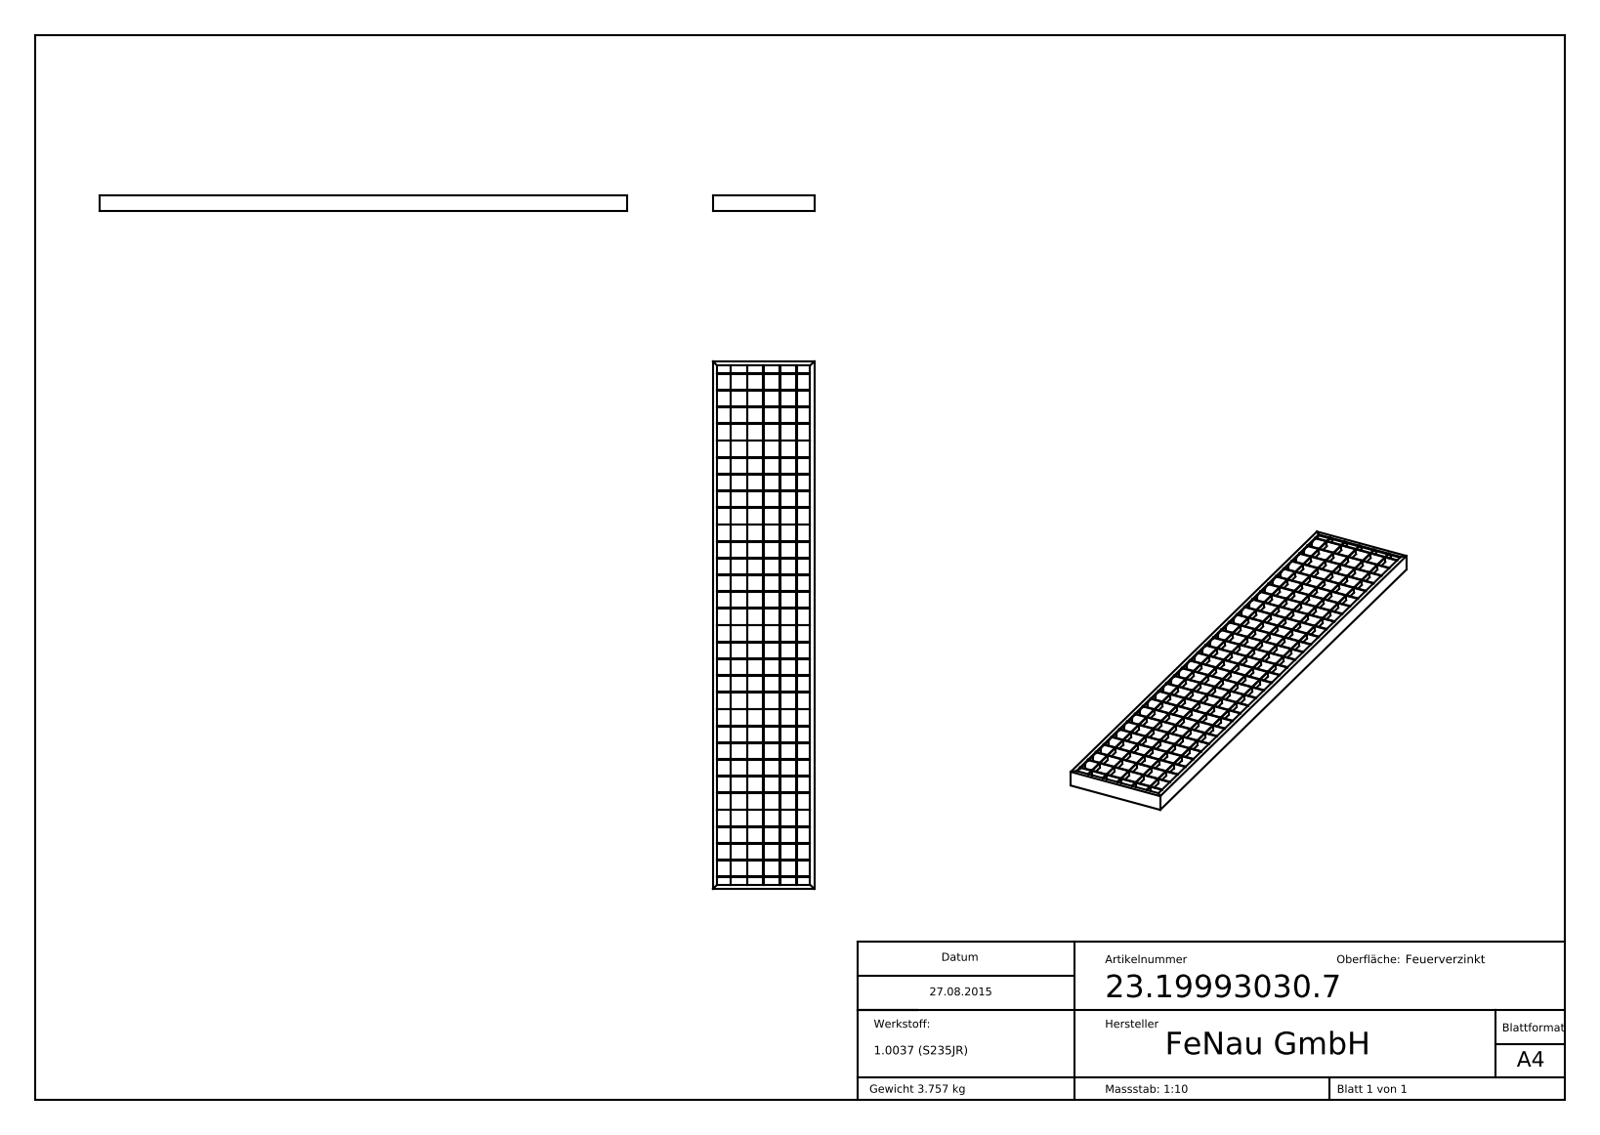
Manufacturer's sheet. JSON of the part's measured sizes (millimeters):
{"part_name": "23-19993030-7", "step_written_by": "SolidWorks 2015 (CONFIG_CONTROL_DESIGN)", "units": "millimeters", "bodies": {"solids": 1, "faces": 896, "planar": 896, "cylindrical": 0, "other": 0}, "overall_size": [990, 190, 30], "volume_mm3": 481685, "surface_area_mm2": 635409, "face_to_face_distances": [63, 31.5, 94.5, 157.5, 31, 126, 62, 189, 30, 220.5]}
